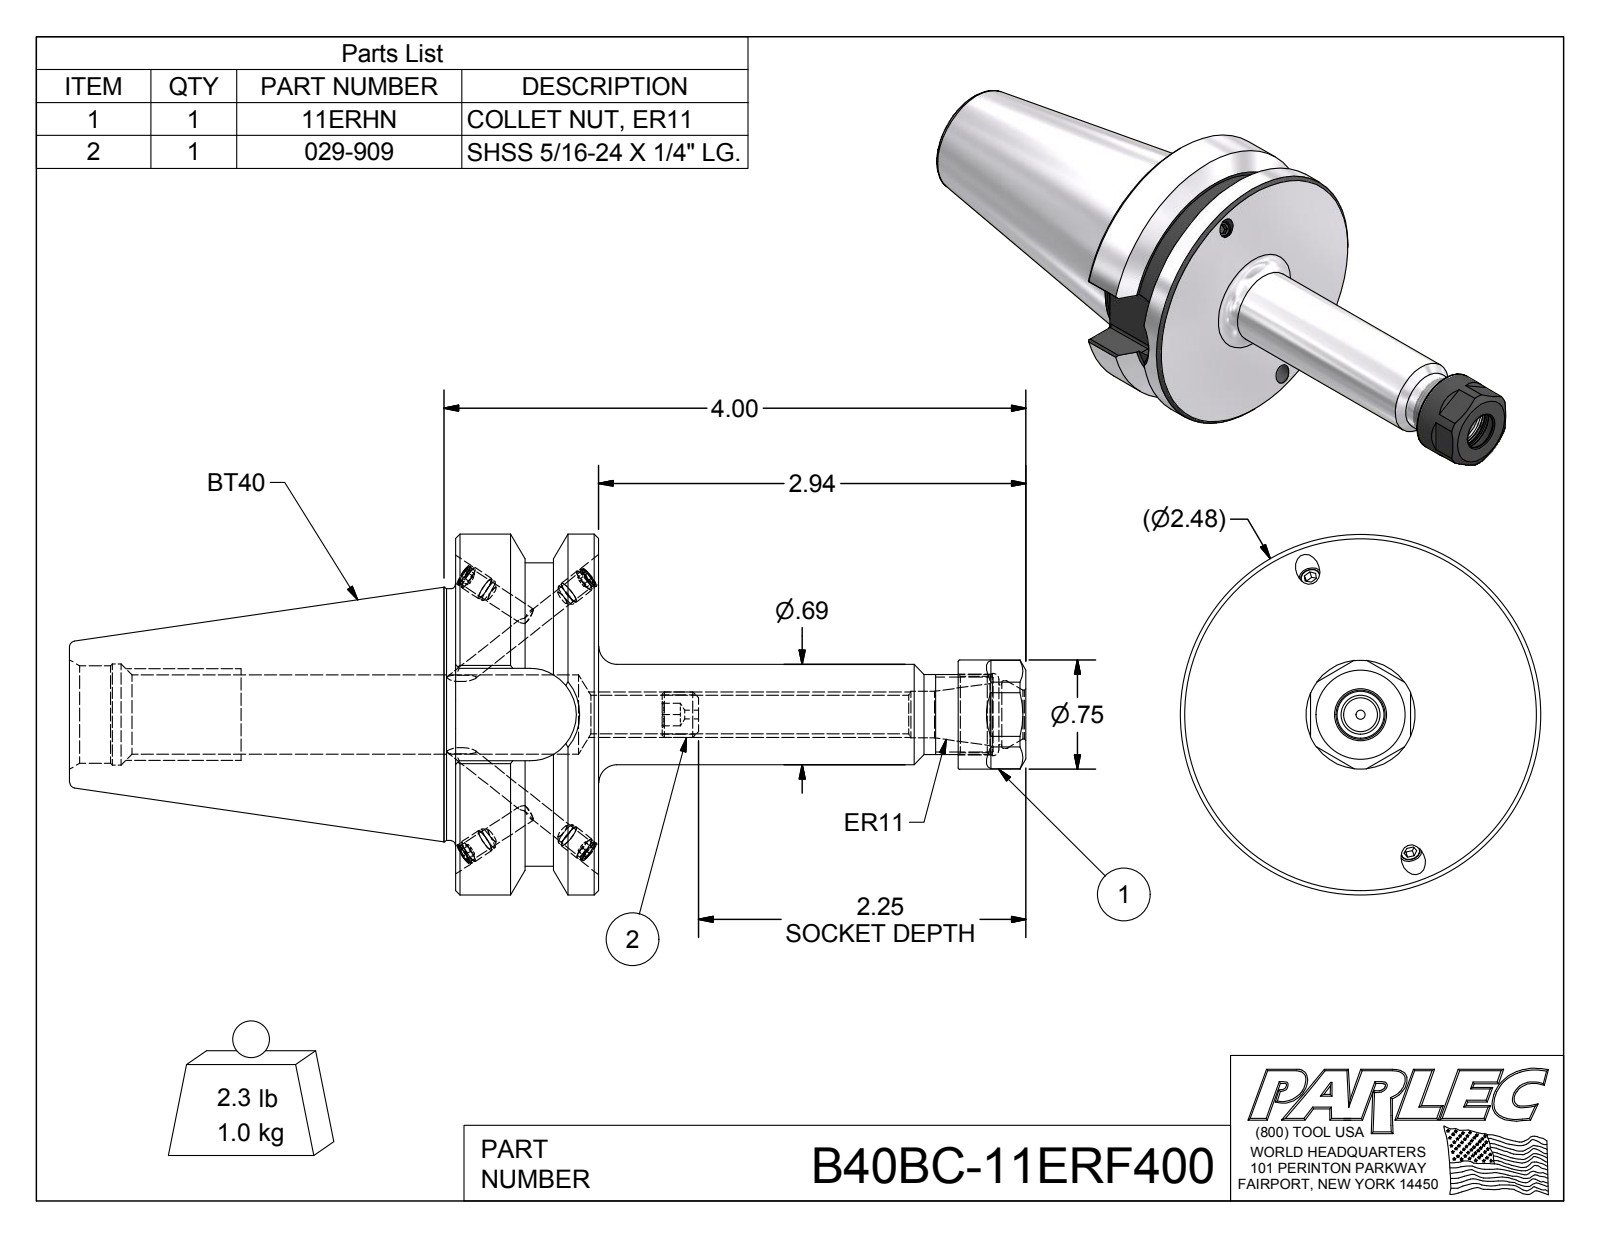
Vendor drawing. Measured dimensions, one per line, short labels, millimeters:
name: B40BC-11ERF400; 029-909; 029-965; 11ERHN
written by: Autodesk Inventor 2016 (AUTOMOTIVE_DESIGN)
unit: mm
bodies: 7 solids, 207 faces (97 planar, 50 cylindrical, 60 other)
size: 167 × 62.99 × 62.99
volume: 133 704 mm³; area: 30 612 mm²
holes: 4× ⌀3.3, 4× ⌀4.1, 1× ⌀1.52, 1× ⌀6.78, 1× ⌀8.13, 1× ⌀8.51, 1× ⌀11.81, 1× ⌀13.33, 1× ⌀13.84, 1× ⌀14.35, 1× ⌀17.01, 1× ⌀17.62
bosses: 4× ⌀4.2, 4× ⌀4, 1× ⌀62.99, 1× ⌀53.01, 1× ⌀43.94, 1× ⌀19.05, 1× ⌀17.48, 1× ⌀14
rounds: 8× R0.51, 1× R8.09
face distances: 24.99, 45.22, 67.39, 92.38, 16.18, 17.48, 167.01, 99.62, 74.63, 155.2
